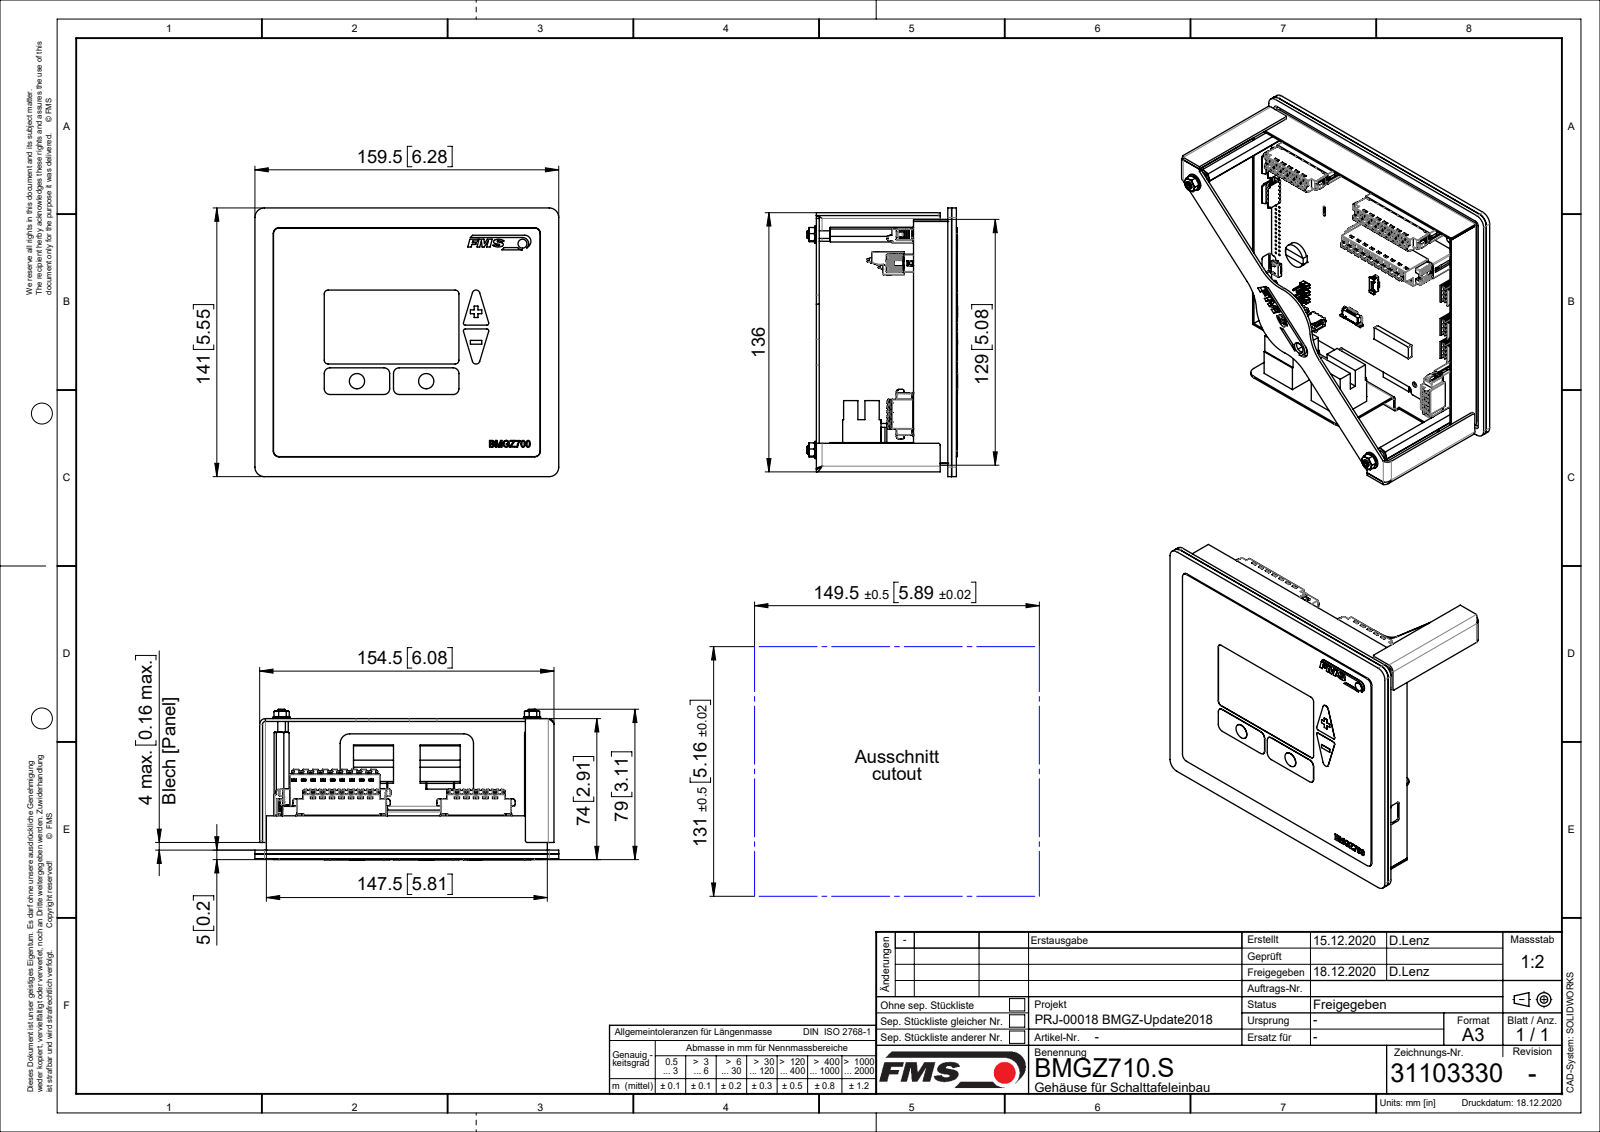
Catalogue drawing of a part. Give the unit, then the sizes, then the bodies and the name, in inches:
Units: inches
Overall size (bounding box): 6.28 × 5.551 × 3.111
Round holes (diameter × count): ⌀0.039 ×32, ⌀0.039 ×32, ⌀0.047 ×18, ⌀0.055 ×17, ⌀0.177 ×8, ⌀0.13 ×4, ⌀0.138 ×4, ⌀0.169 ×4, ⌀0.173 ×4, ⌀0.035 ×2, ⌀0.079 ×2, ⌀0.118 ×2
Round bosses / shafts (diameter × count): ⌀0.024 ×60, ⌀0.025 ×12, ⌀0.354 ×4, ⌀0.157 ×4, ⌀0.315 ×2, ⌀0.512 ×1, ⌀0.184 ×1, ⌀0.079 ×1
Partial cylindrical surfaces — rounded edges, fillets, slot ends (radius × count): R0.008 ×584, R0.012 ×412, R0.004 ×265, R0.02 ×204, R0.039 ×192, R0.018 ×72, R0.006 ×49, R0.01 ×40
Main face-to-face distances: 0.362, 0.307, 0.055, 0.079, 0.039, 0.406, 0.351, 0.044, 0.441, 0.386
Hole centre spacings: 0.2, 0.197, 0.204, 0.4, 0.394, 0.348, 0.6, 0.53
Volume: 14.76 in³ · Surface area: 427.2 in²
Bodies: 78 solids, 13667 faces (8474 planar, 3682 cylindrical, 1511 other)
Part name (STEP PRODUCT): 6kt-Mu ISO4032_M4; 31103344_01; 31103343_01; PEM_Einpress-Gew-Bolzen_PEM Einpress-Gew.Bolzen M4x 6 vz - min.1 (+8 more)
STEP written by: SolidWorks 2018 (CONFIG_CONTROL_DESIGN)
